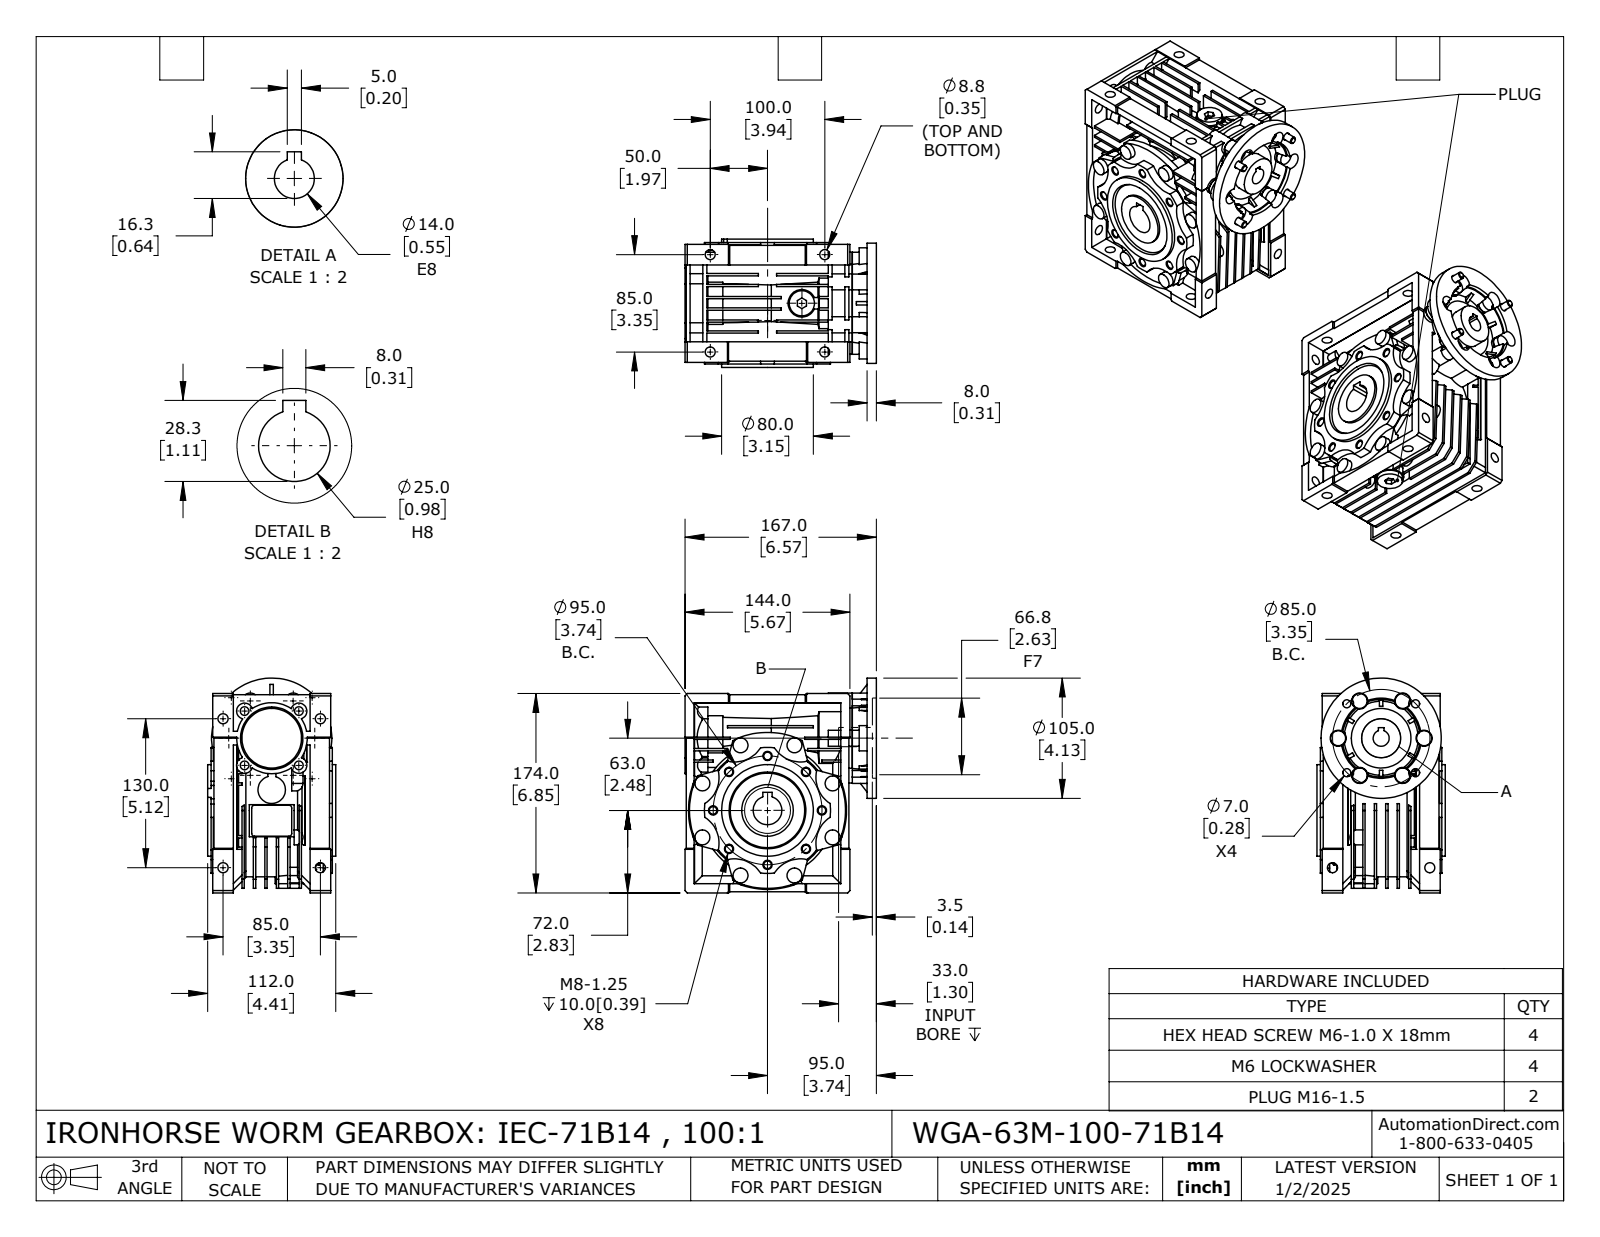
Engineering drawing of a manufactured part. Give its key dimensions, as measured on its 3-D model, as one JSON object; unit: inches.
{"part_name": "WGA-63M-100-71B14", "step_written_by": "SolidWorks 2024 (CONFIG_CONTROL_DESIGN)", "units": "inches", "bodies": {"solids": 16, "faces": 1428, "planar": 836, "cylindrical": 417, "other": 175}, "overall_size": [7.382, 6.909, 4.409], "volume_in3": 110.9, "surface_area_in2": 529.7, "round_holes": [[0.262, 8], [0.346, 8], [0.24, 4], [0.276, 4], [0.298, 4], [0.571, 2], [0.551, 1], [0.591, 1], [0.984, 1], [1.339, 1], [1.457, 1], [1.772, 1]], "round_bosses_or_shafts": [[0.512, 14], [0.551, 4], [0.48, 4], [0.236, 4], [0.945, 3], [0.866, 2], [0.622, 2], [0.539, 2]], "partial_cylinders_radius": [[0.276, 12], [1.063, 8], [0.275, 6], [0.433, 6], [0.098, 4], [0.236, 4], [0.329, 1], [1.161, 1]], "face_to_face_distances": [0.394, 0.315, 0.787, 0.079, 1.181, 0.276, 0.472, 1.575, 0.709, 0.039], "hole_center_spacings": [1.431, 1.87, 2.131, 2.645, 3.456, 0.354, 1.319, 1.673]}
